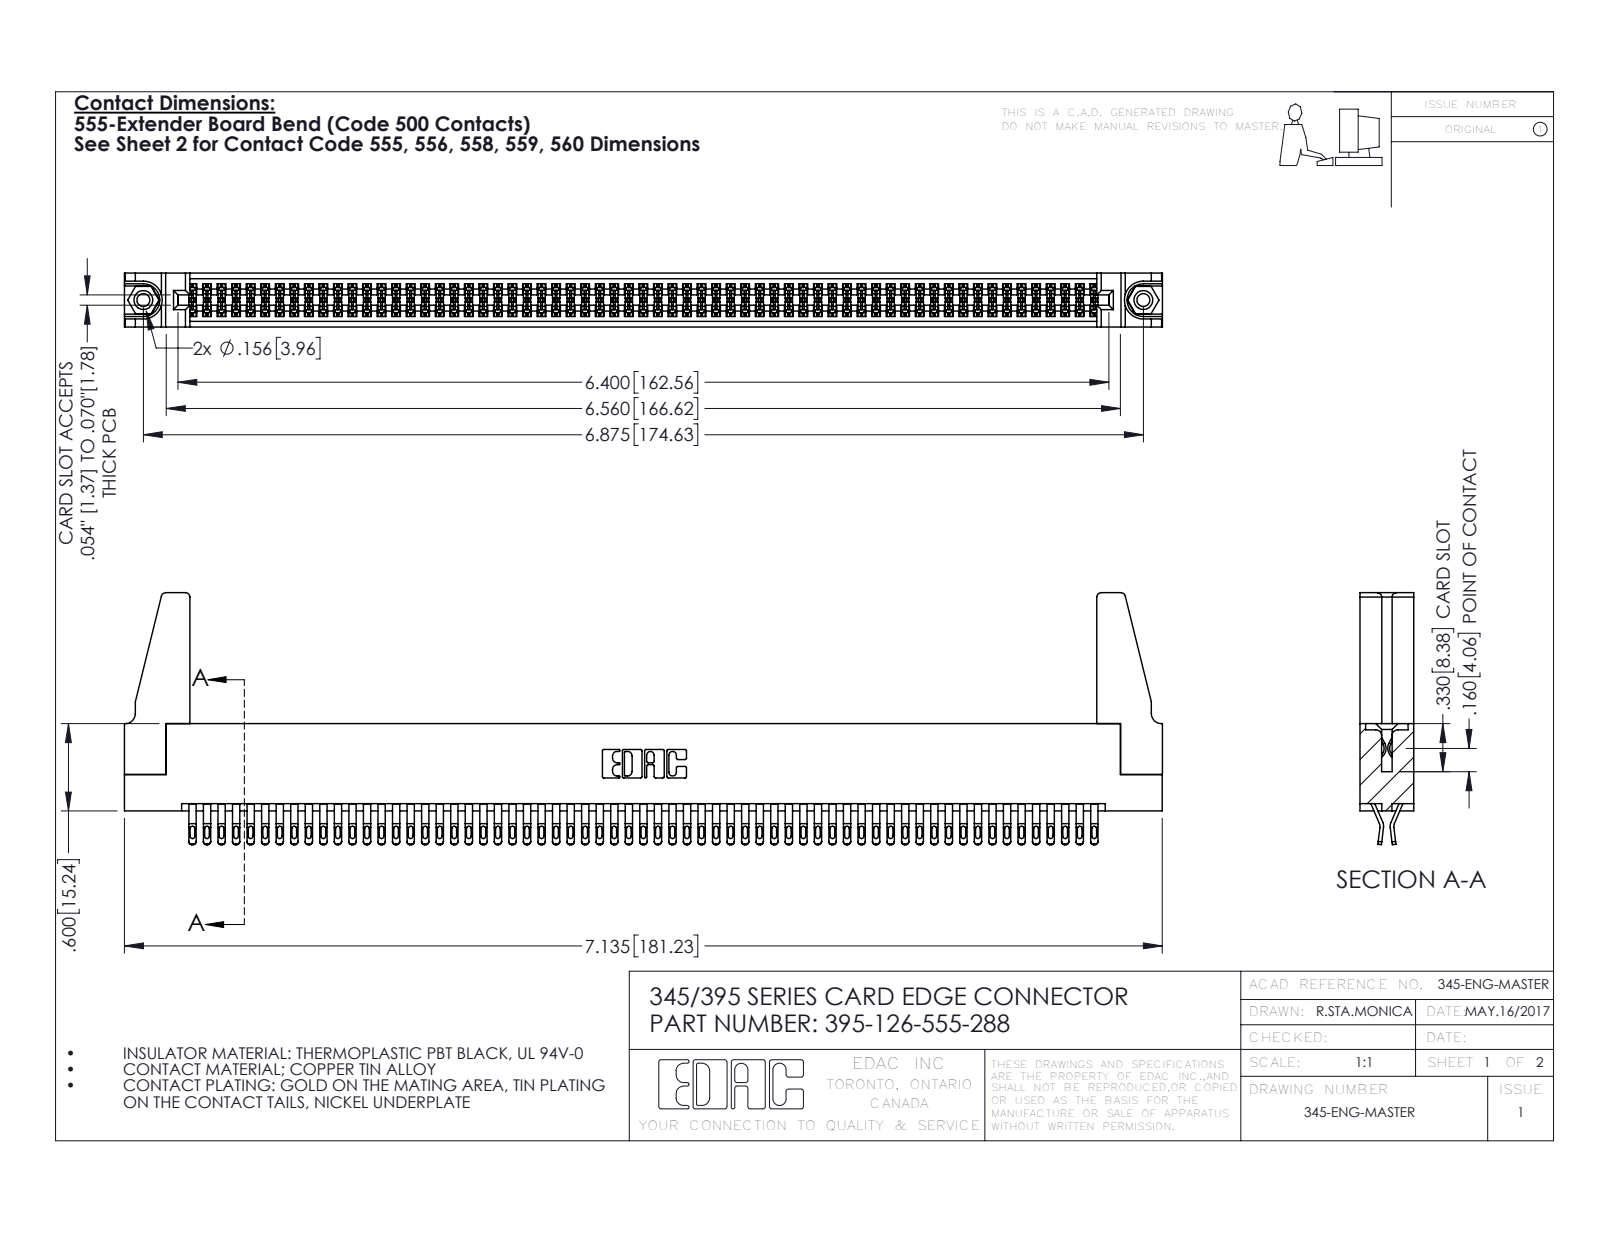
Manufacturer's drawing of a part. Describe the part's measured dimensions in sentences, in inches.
The part is named "345 Part_Flush Mounting Lugs - 0.156 Dia-TH; 345-292-001_555 Tail; 345-220-078_345-220-088; 395-126-555-288 (+1 more)". Its 3-D file was written by "SolidWorks 2016 (CONFIG_CONTROL_DESIGN)". It is 131 solids with 7306 faces: 4058 planar, 3232 cylindrical and 16 other. Overall it measures 7.136 by 1.732 by 0.37 inches. Its volume is 1.307 cubic inches and its surface area 49.07 square inches. Round holes: 2 of diameter 0.089, 2 of diameter 0.125, 2 of diameter 0.156, 1 of diameter 0.064. Round bosses or shafts: 2 of diameter 0.155. Partial cylindrical surfaces (rounded edges, fillets, slot ends): 315 of radius 0.016, 252 of radius 0.02, 189 of radius 0.006, 22 of radius 0.01, 8 of radius 0.03, 6 of radius 0.007, 6 of radius 0.031, 3 of radius 0.026. The main face-to-face distances are 0.072, 0.298, 0.37, 0.025, 0.2, 0.098, 0.272, 0.225, 0.175, 0.149. The hole center spacings are 0.27, 6.639, 6.875.
